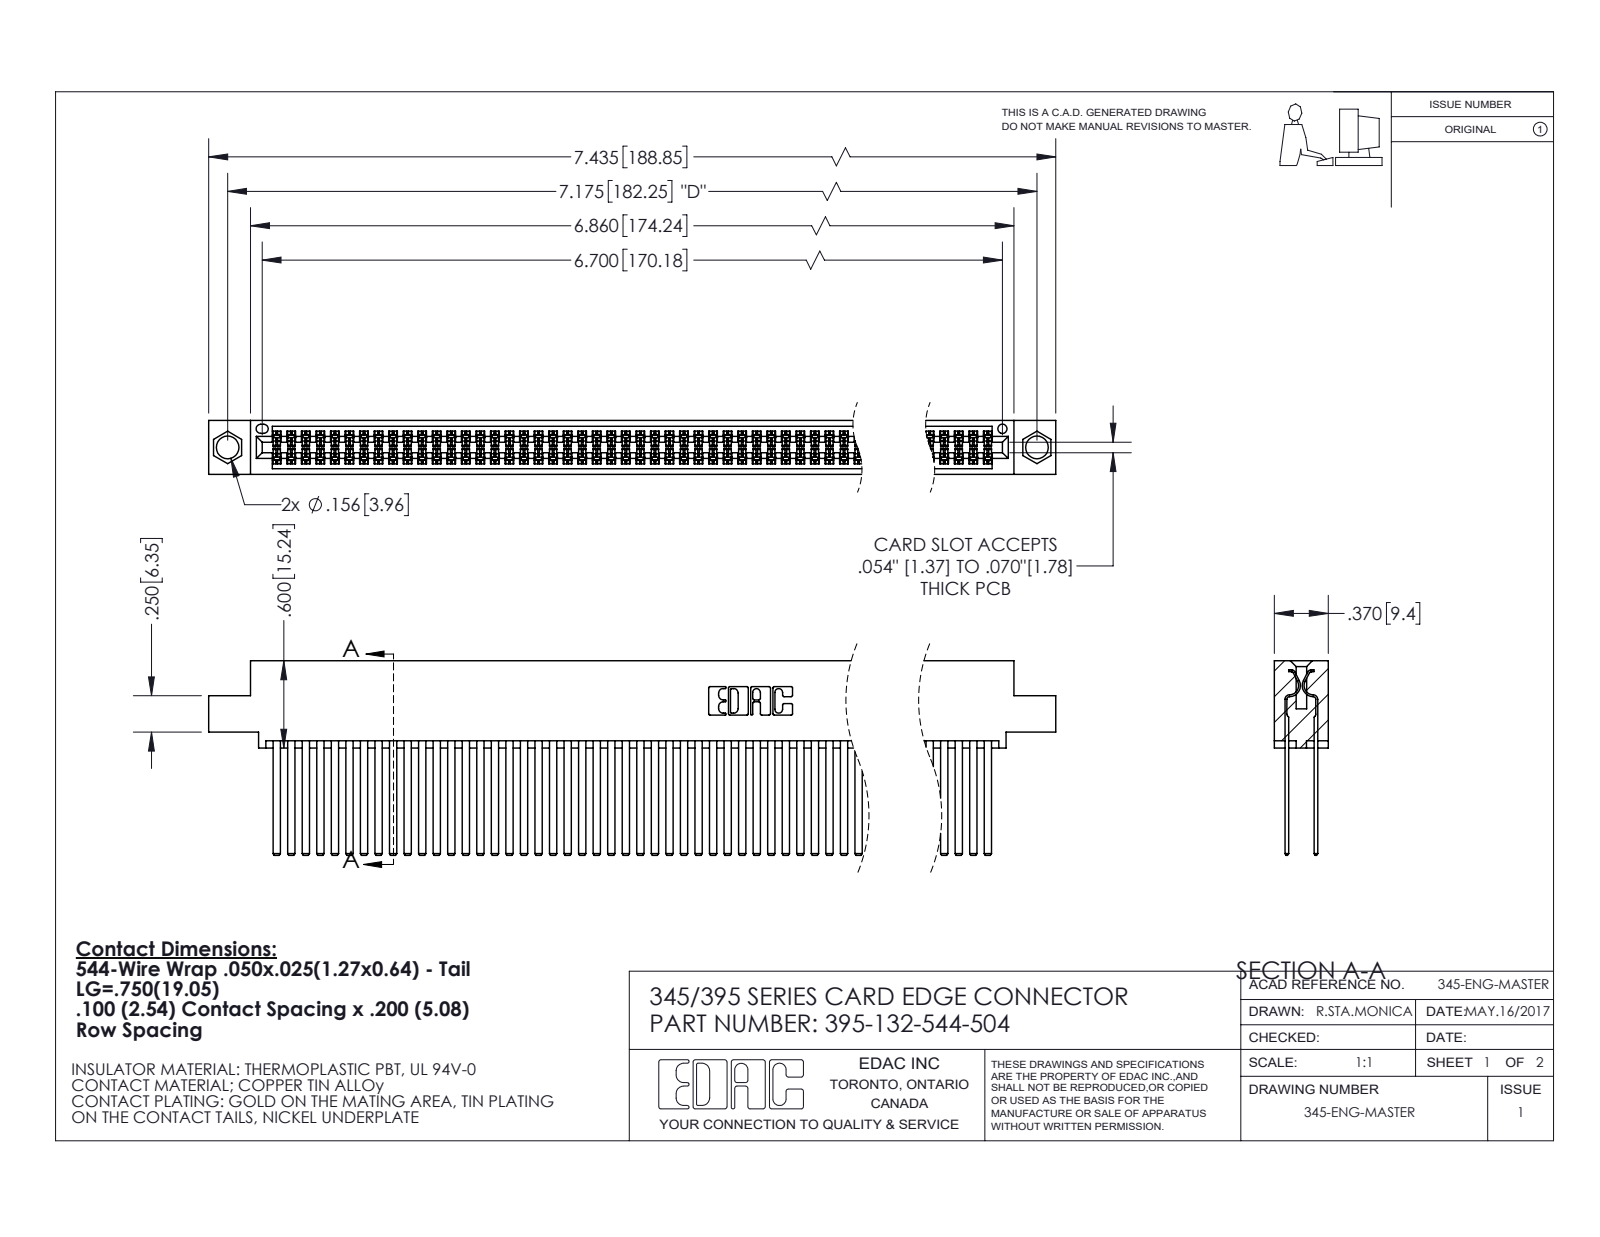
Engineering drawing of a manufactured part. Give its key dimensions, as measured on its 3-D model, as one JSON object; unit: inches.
{"part_name": "345 Part_0.110 Offset - 0.156 Dia-TI; 395-132-544-504; 345-292-001_345-293-144", "step_written_by": "SolidWorks 2020 (CONFIG_CONTROL_DESIGN)", "units": "inches", "bodies": {"solids": 133, "faces": 5952, "planar": 3926, "cylindrical": 2026, "other": 0}, "overall_size": [7.435, 1.337, 0.37], "volume_in3": 1.235, "surface_area_in2": 55.41, "round_holes": [[0.156, 2], [0.064, 1]], "partial_cylinders_radius": [[0.006, 198], [0.01, 22], [0.007, 6], [0.031, 6], [0.026, 3], [0.014, 2], [0.019, 2], [0.022, 2]], "face_to_face_distances": [0.2, 0.025, 0.298, 0.072, 0.098, 0.272, 0.225, 0.175, 0.37, 0.149], "hole_center_spacings": [0.27, 6.939, 7.175]}
